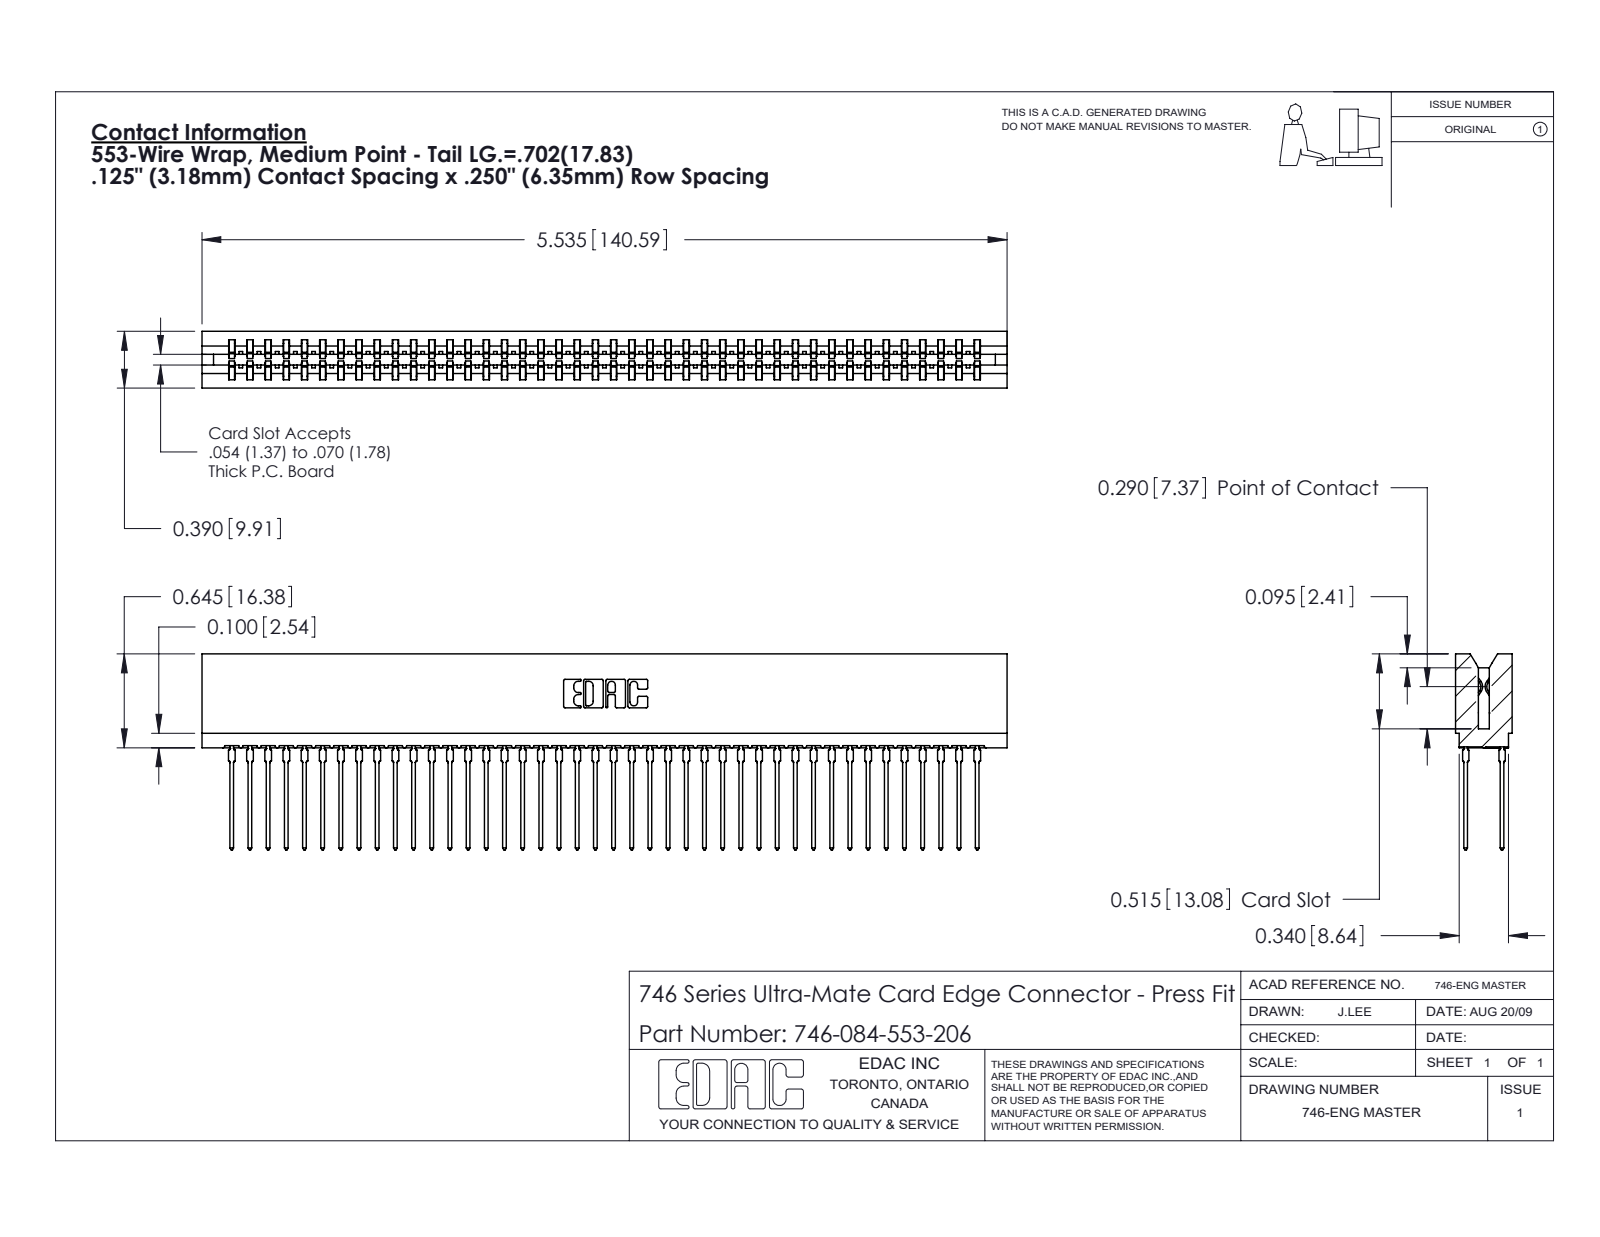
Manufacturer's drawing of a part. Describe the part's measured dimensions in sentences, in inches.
The part is named "746-292-001_553; 746 Part_.515 Slot Depth - 06; 746-084-553-206". Its 3-D file was written by "SolidWorks 2020 (CONFIG_CONTROL_DESIGN)". It is 85 solids with 7616 faces: 3920 planar, 1512 cylindrical and 2184 other. Overall it measures 5.535 by 1.346 by 0.39 inches. Its volume is 0.941 cubic inches and its surface area 41.06 square inches. Partial cylindrical surfaces (rounded edges, fillets, slot ends): 168 of radius 0.021, 43 of radius 0.015, 22 of radius 0.01, 8 of radius 0.005, 8 of radius 0.011, 6 of radius 0.007, 6 of radius 0.031, 3 of radius 0.026. The main face-to-face distances are 0.057, 0.333, 0.25, 0.025, 0.307, 0.39, 0.083, 0.275, 0.174, 0.158.
